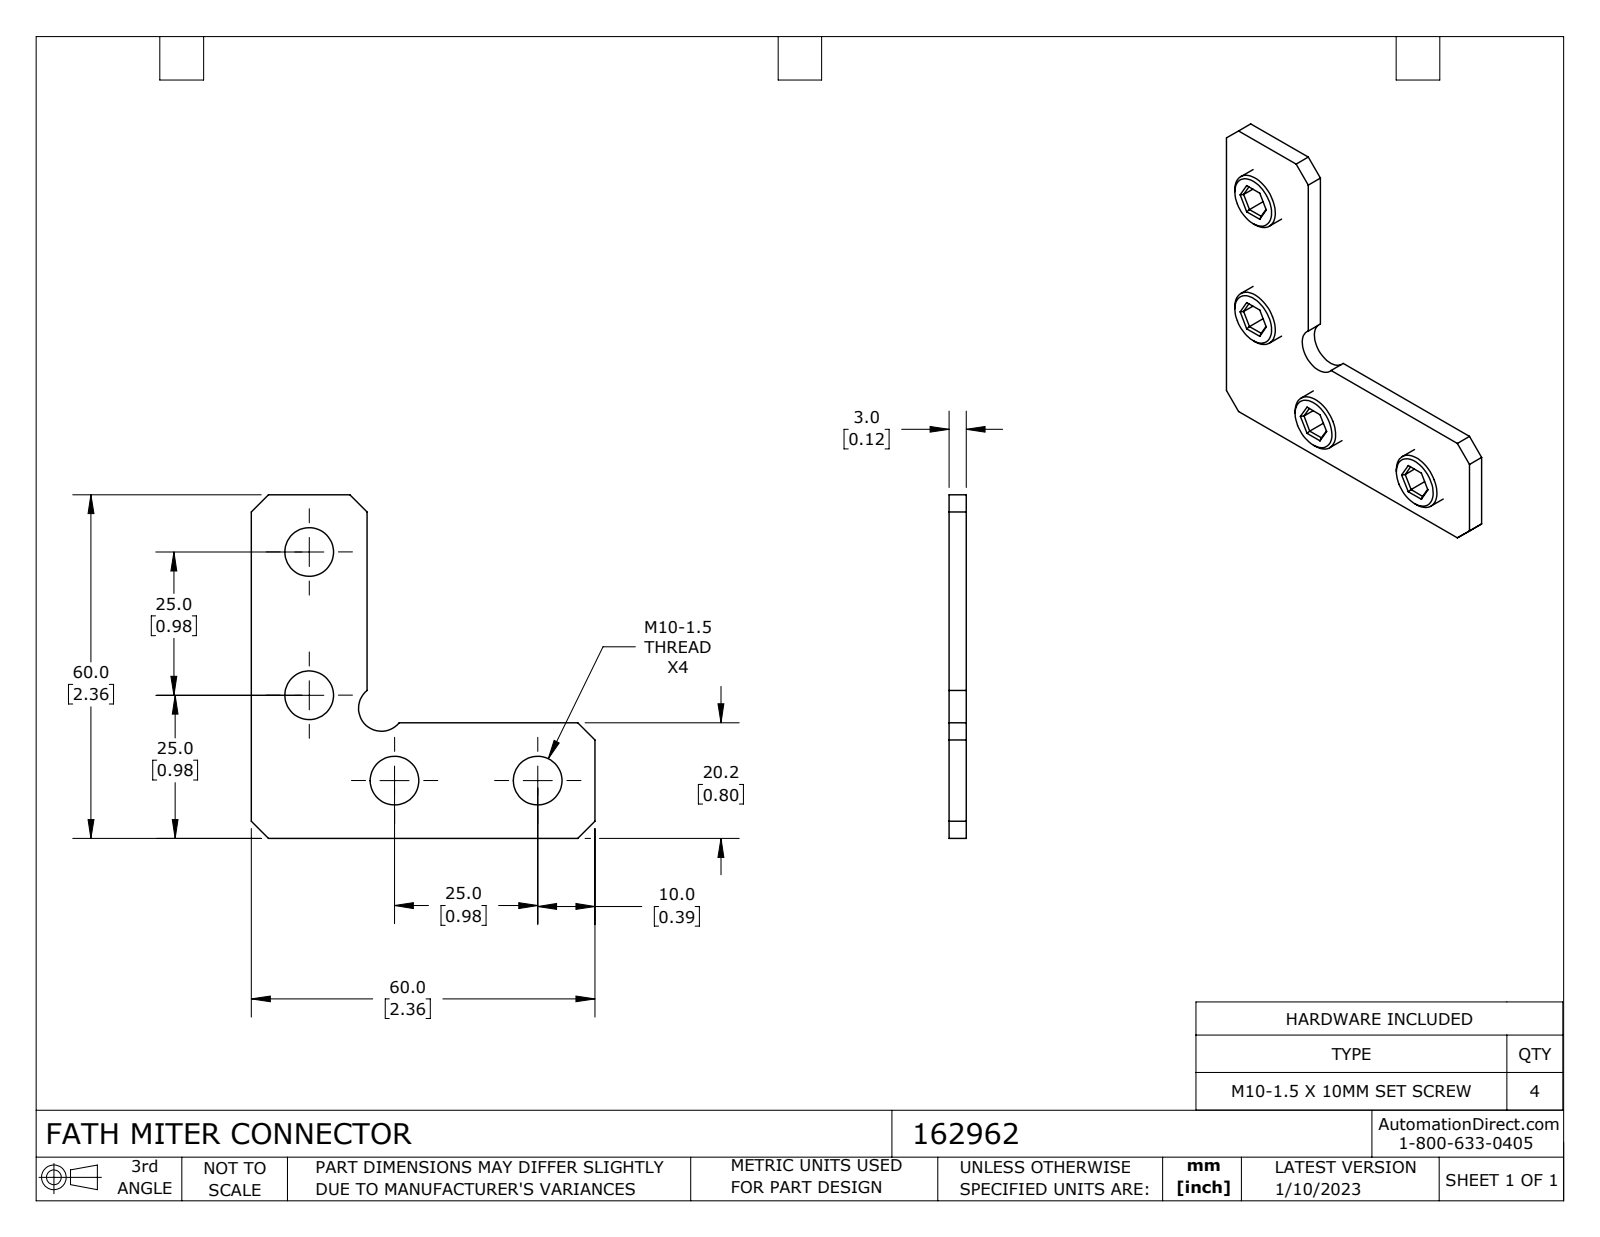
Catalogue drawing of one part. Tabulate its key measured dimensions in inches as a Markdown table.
| quantity | value |
| --- | --- |
| part name | 162962 |
| STEP written by | SolidWorks 2021 (CONFIG_CONTROL_DESIGN) |
| units | inches |
| bodies | 5 solids, 135 faces (93 planar, 18 cylindrical, 24 other) |
| overall size | 2.362 × 2.362 × 0.394 |
| volume | 0.448 in³ |
| surface area | 9.772 in² |
| round holes (diameter × count) | 0.335 × 4 |
| round bosses / shafts (diameter × count) | 0.394 × 4 |
| partial cylindrical surfaces (radius × count) | 0.157 × 1 |
| main face-to-face distances | 0.118, 0.795, 0.138, 0.256, 0.197, 2.362, 1.567, 0.492, 0.852, 0.299 |
| hole center spacings | 0.984, 1.677, 0.83, 2.222 |
